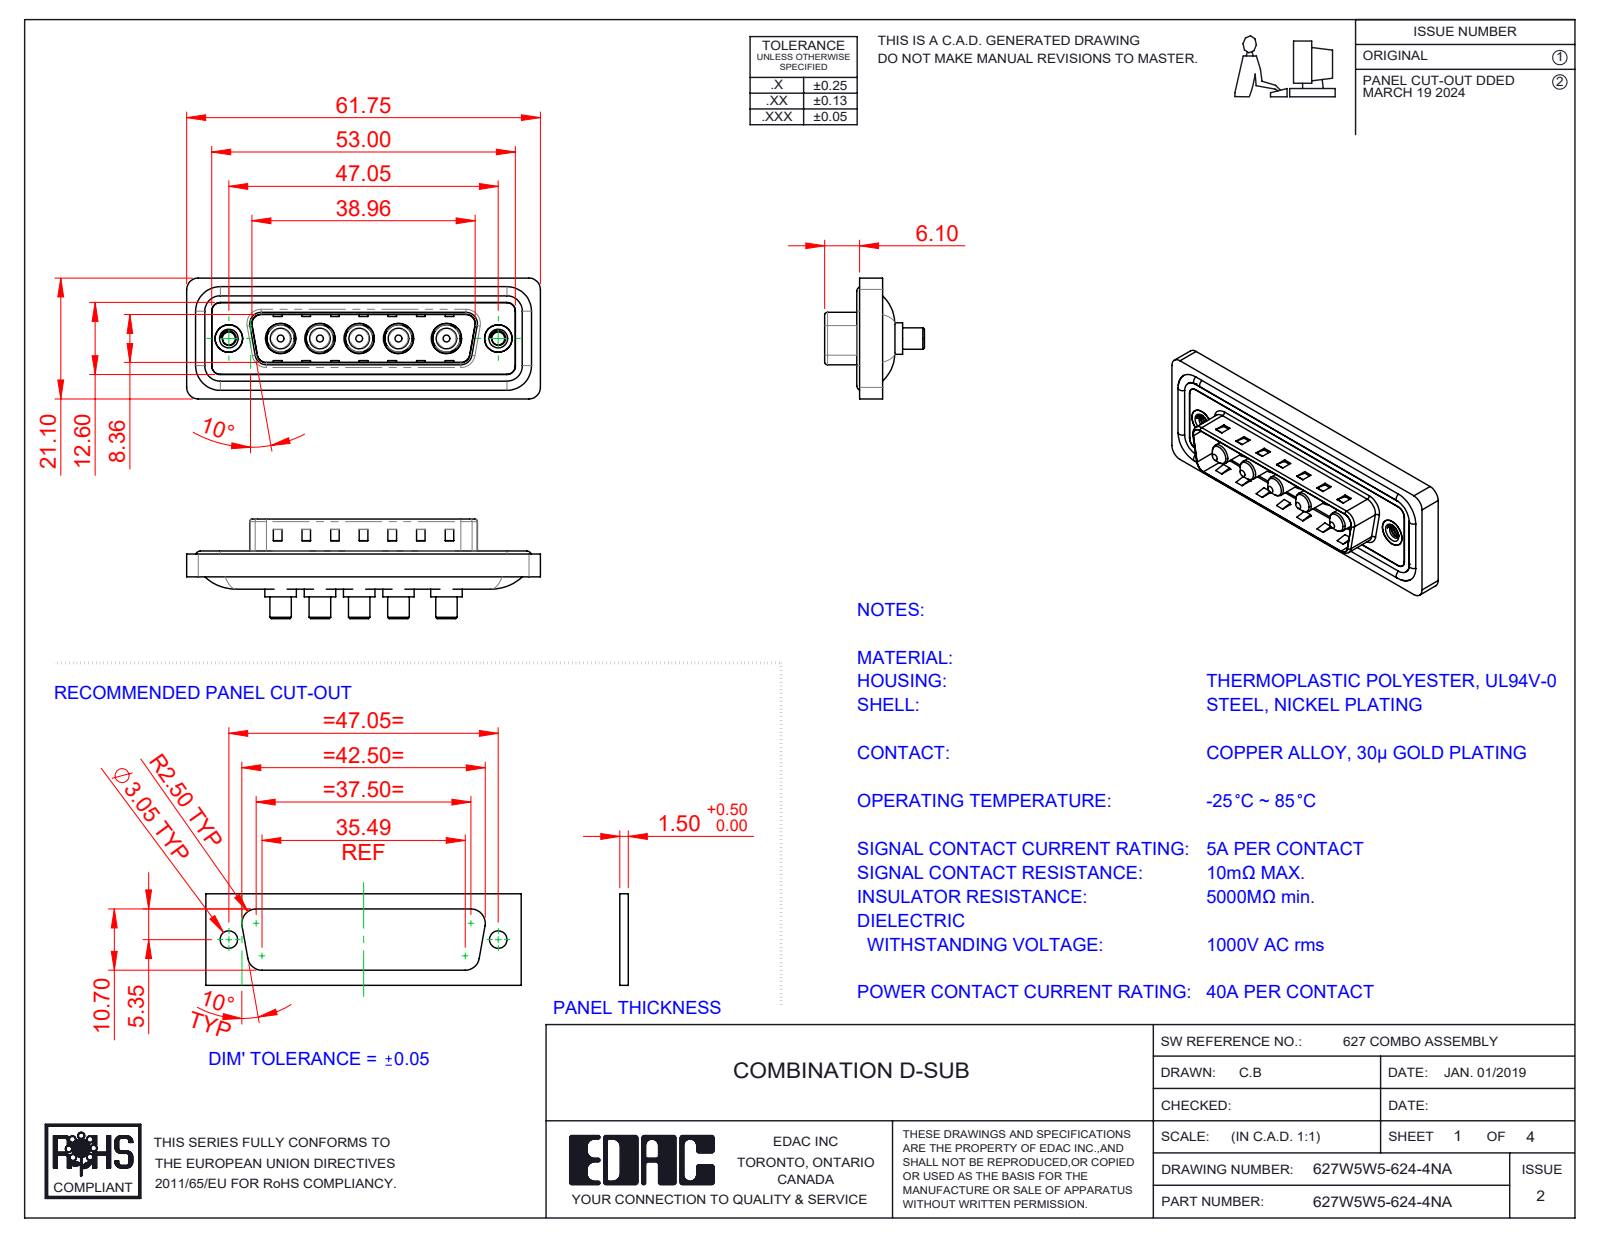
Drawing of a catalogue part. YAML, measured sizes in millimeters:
part_name: "627Combo Housing_5W5; 627W5W5-624-4NA; 627Combo Shell Front_25 Contacts; 627Combo Shell Rear_25 Contacts (+3 more)"
step_written_by: "SolidWorks 2023 (CONFIG_CONTROL_DESIGN)"
units: millimeters
bodies: {solids: 17, faces: 676, planar: 259, cylindrical: 285, other: 132}
overall_size: [61.75, 21.1, 17.4]
volume: 7567
surface_area: 11848
round_holes:
  - {diameter: 4.85, count: 5}
  - {diameter: 5.3, count: 5}
  - {diameter: 2.26, count: 2}
  - {diameter: 4, count: 2}
  - {diameter: 4.8, count: 2}
  - {diameter: 5, count: 2}
round_bosses_or_shafts:
  - {diameter: 5.5, count: 5}
  - {diameter: 5.2, count: 5}
  - {diameter: 4.75, count: 5}
  - {diameter: 3.75, count: 5}
  - {diameter: 3.6, count: 5}
  - {diameter: 1.6, count: 4}
  - {diameter: 4.9, count: 2}
partial_cylinders:
  - {radius: 1.5, count: 22}
  - {radius: 2, count: 18}
  - {radius: 0.5, count: 8}
  - {radius: 1.6, count: 8}
  - {radius: 2.1, count: 5}
  - {radius: 0.25, count: 4}
  - {radius: 0.6, count: 4}
  - {radius: 0.65, count: 4}
face_to_face_distances: [0.4, 1.5, 0.5, 1.1, 3.1, 1.6, 2.9, 0.82, 9.58, 5.65]
hole_center_spacings: [6.86, 9.04, 13.73, 38.01, 6.87, 8.37, 8.38, 9.05]
